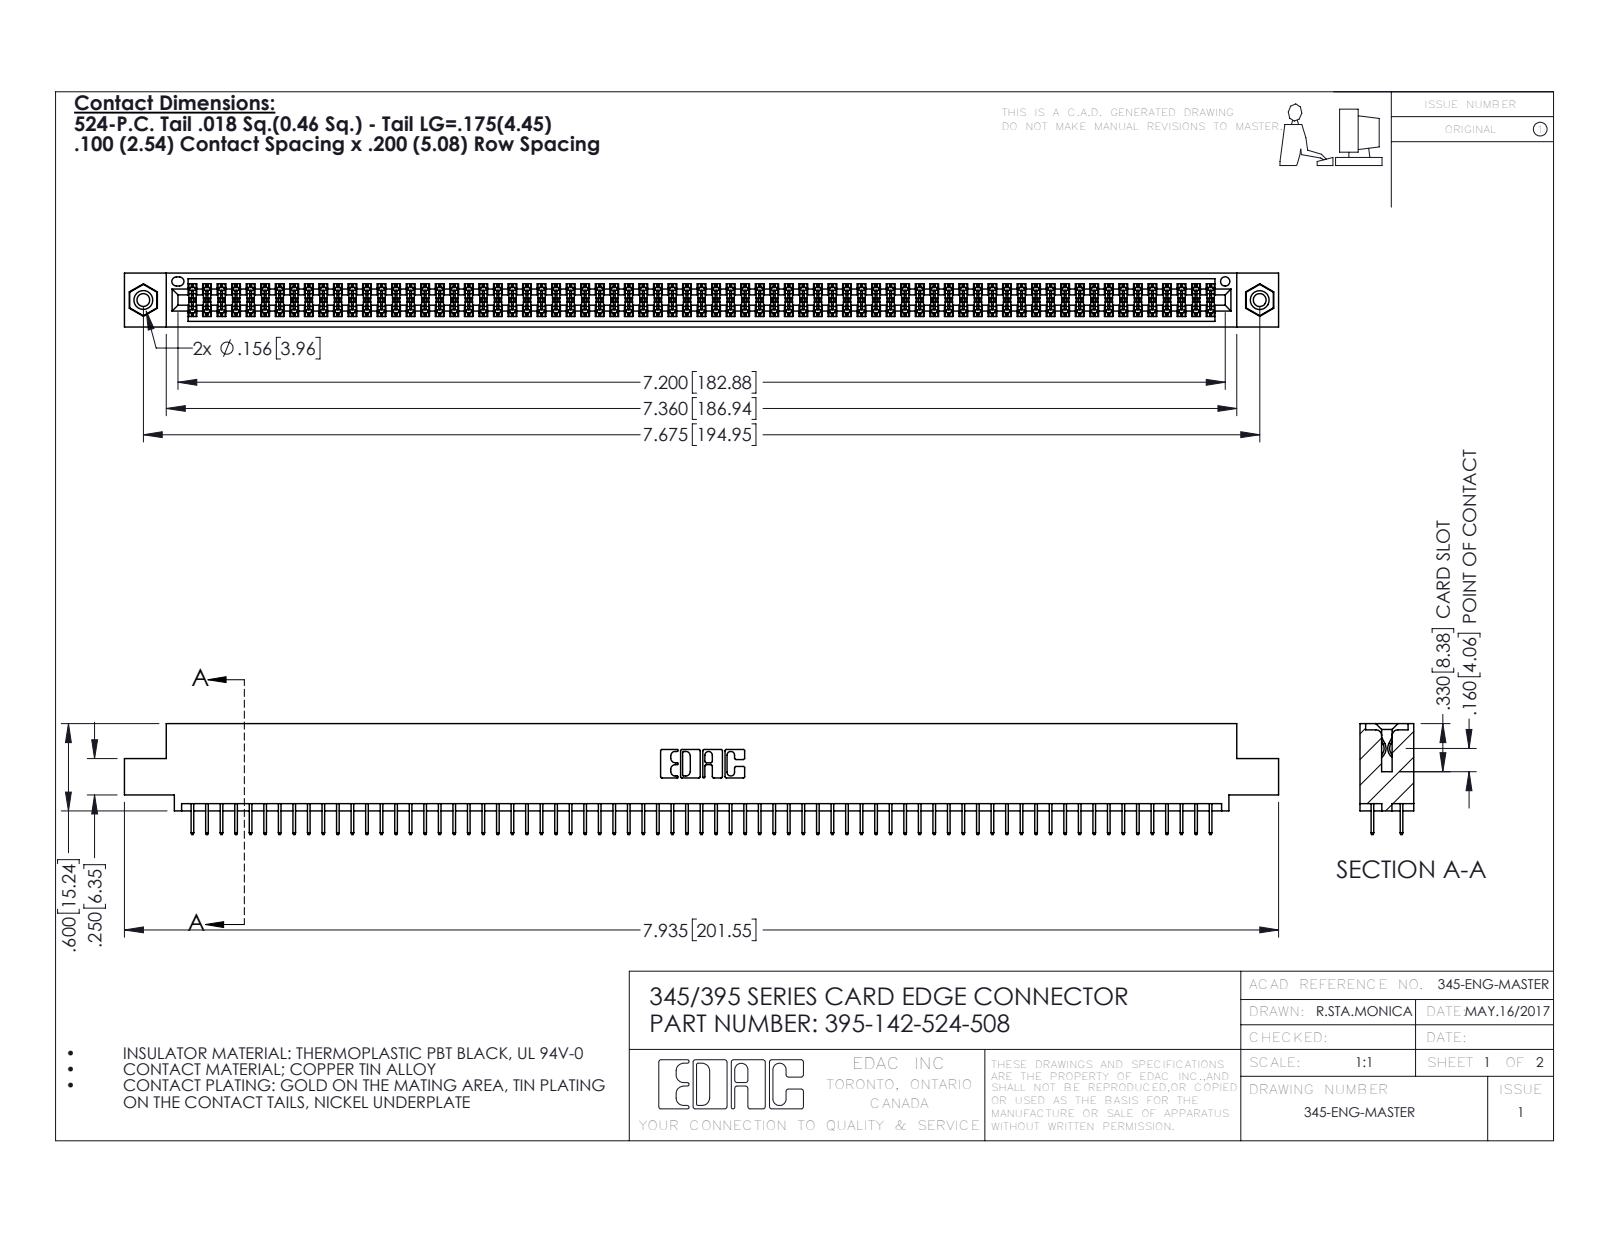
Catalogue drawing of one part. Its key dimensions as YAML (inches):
part_name: "345-250-001_345-250-003-102; 395-142-524-508; 345 Part_0.110 Offset - 0.156 Dia-TI; 345-292-001_345-293-124"
step_written_by: "SolidWorks 2016 (CONFIG_CONTROL_DESIGN)"
units: inches
bodies: {solids: 145, faces: 7858, planar: 5654, cylindrical: 2188, other: 16}
overall_size: [7.935, 0.762, 0.37]
volume: 1.193
surface_area: 44.96
round_holes:
  - {diameter: 0.089, count: 2}
  - {diameter: 0.125, count: 2}
  - {diameter: 0.156, count: 2}
  - {diameter: 0.064, count: 1}
round_bosses_or_shafts:
  - {diameter: 0.155, count: 2}
partial_cylinders:
  - {radius: 0.006, count: 213}
  - {radius: 0.01, count: 22}
  - {radius: 0.007, count: 6}
  - {radius: 0.031, count: 6}
  - {radius: 0.026, count: 3}
  - {radius: 0.014, count: 2}
  - {radius: 0.019, count: 2}
  - {radius: 0.022, count: 2}
face_to_face_distances: [0.072, 0.298, 0.2, 0.37, 0.098, 0.272, 0.025, 0.225, 0.072, 0.175]
hole_center_spacings: [0.27, 7.439, 7.675]
